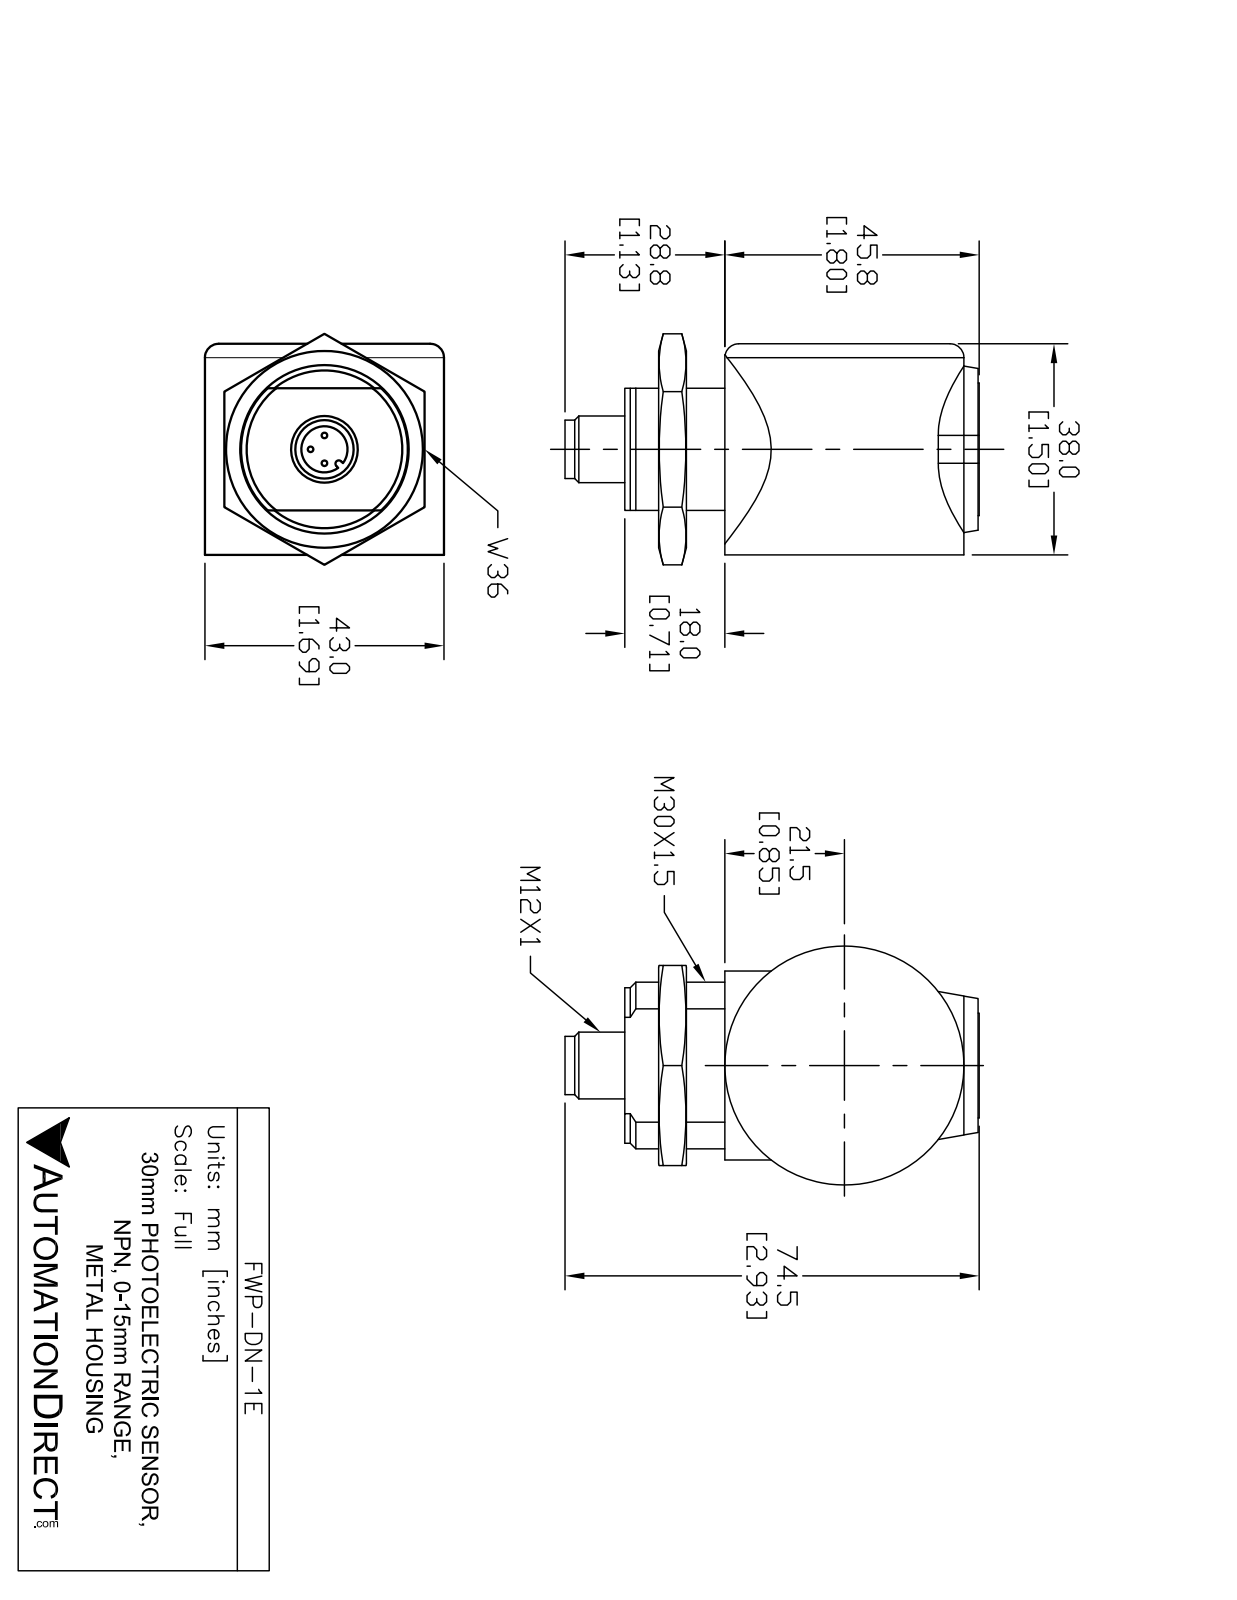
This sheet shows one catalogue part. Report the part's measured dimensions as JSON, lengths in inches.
{"part_name": "FWP-DN-1E", "step_written_by": "SolidWorks 2013 (AUTOMOTIVE_DESIGN)", "units": "inches", "bodies": {"solids": 1, "faces": 60, "planar": 29, "cylindrical": 24, "other": 7}, "overall_size": [2.928, 1.69, 1.49], "volume_in3": 4.417, "surface_area_in2": 19.34, "round_holes": [[0.315, 1]], "round_bosses_or_shafts": [[0.04, 3], [1.69, 1], [0.47, 1], [0.39, 1]], "partial_cylinders_radius": [[0.64, 2], [0.025, 1], [0.545, 1], [0.587, 1]], "face_to_face_distances": [1.49, 2.518, 0.11, 2.408, 0.3, 0.19, 2.218, 1.178, 0.312, 0.312]}
